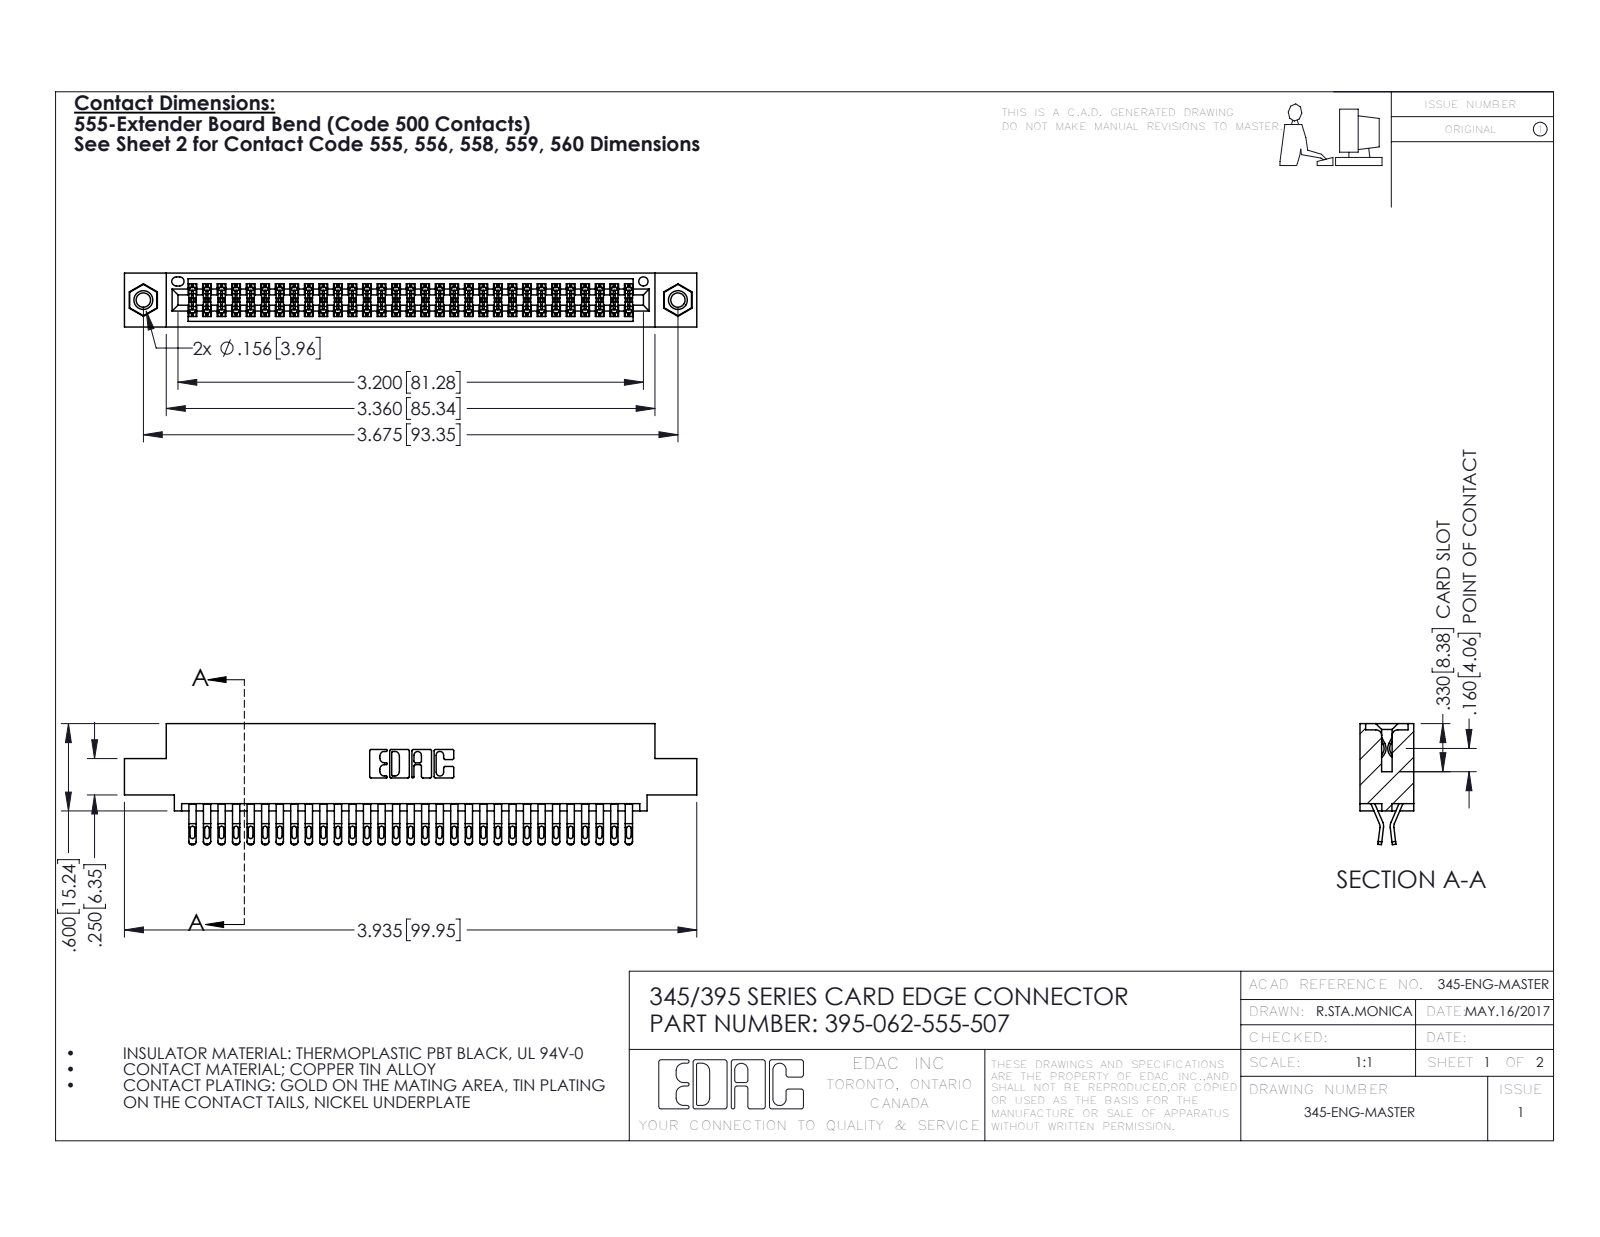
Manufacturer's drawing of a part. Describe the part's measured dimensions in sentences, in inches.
The part is named "345 Part_0.110 Offset - 0.156 Dia-TI; 345-250-001_345-250-005-103; 395-062-555-507; 345-292-001_555 Tail". Its 3-D file was written by "SolidWorks 2016 (CONFIG_CONTROL_DESIGN)". It is 65 solids with 3662 faces: 2038 planar, 1608 cylindrical and 16 other. Overall it measures 3.935 by 0.832 by 0.37 inches. Its volume is 0.592 cubic inches and its surface area 23.05 square inches. Round holes: 2 of diameter 0.098, 2 of diameter 0.125, 2 of diameter 0.156, 1 of diameter 0.064. Round bosses or shafts: 2 of diameter 0.155. Partial cylindrical surfaces (rounded edges, fillets, slot ends): 155 of radius 0.016, 124 of radius 0.02, 93 of radius 0.006, 22 of radius 0.01, 6 of radius 0.007, 6 of radius 0.031, 3 of radius 0.026, 2 of radius 0.01. The main face-to-face distances are 0.072, 0.298, 0.2, 0.37, 0.025, 0.098, 0.272, 0.225, 0.175, 0.149. The hole center spacings are 0.27, 3.44, 3.675.
